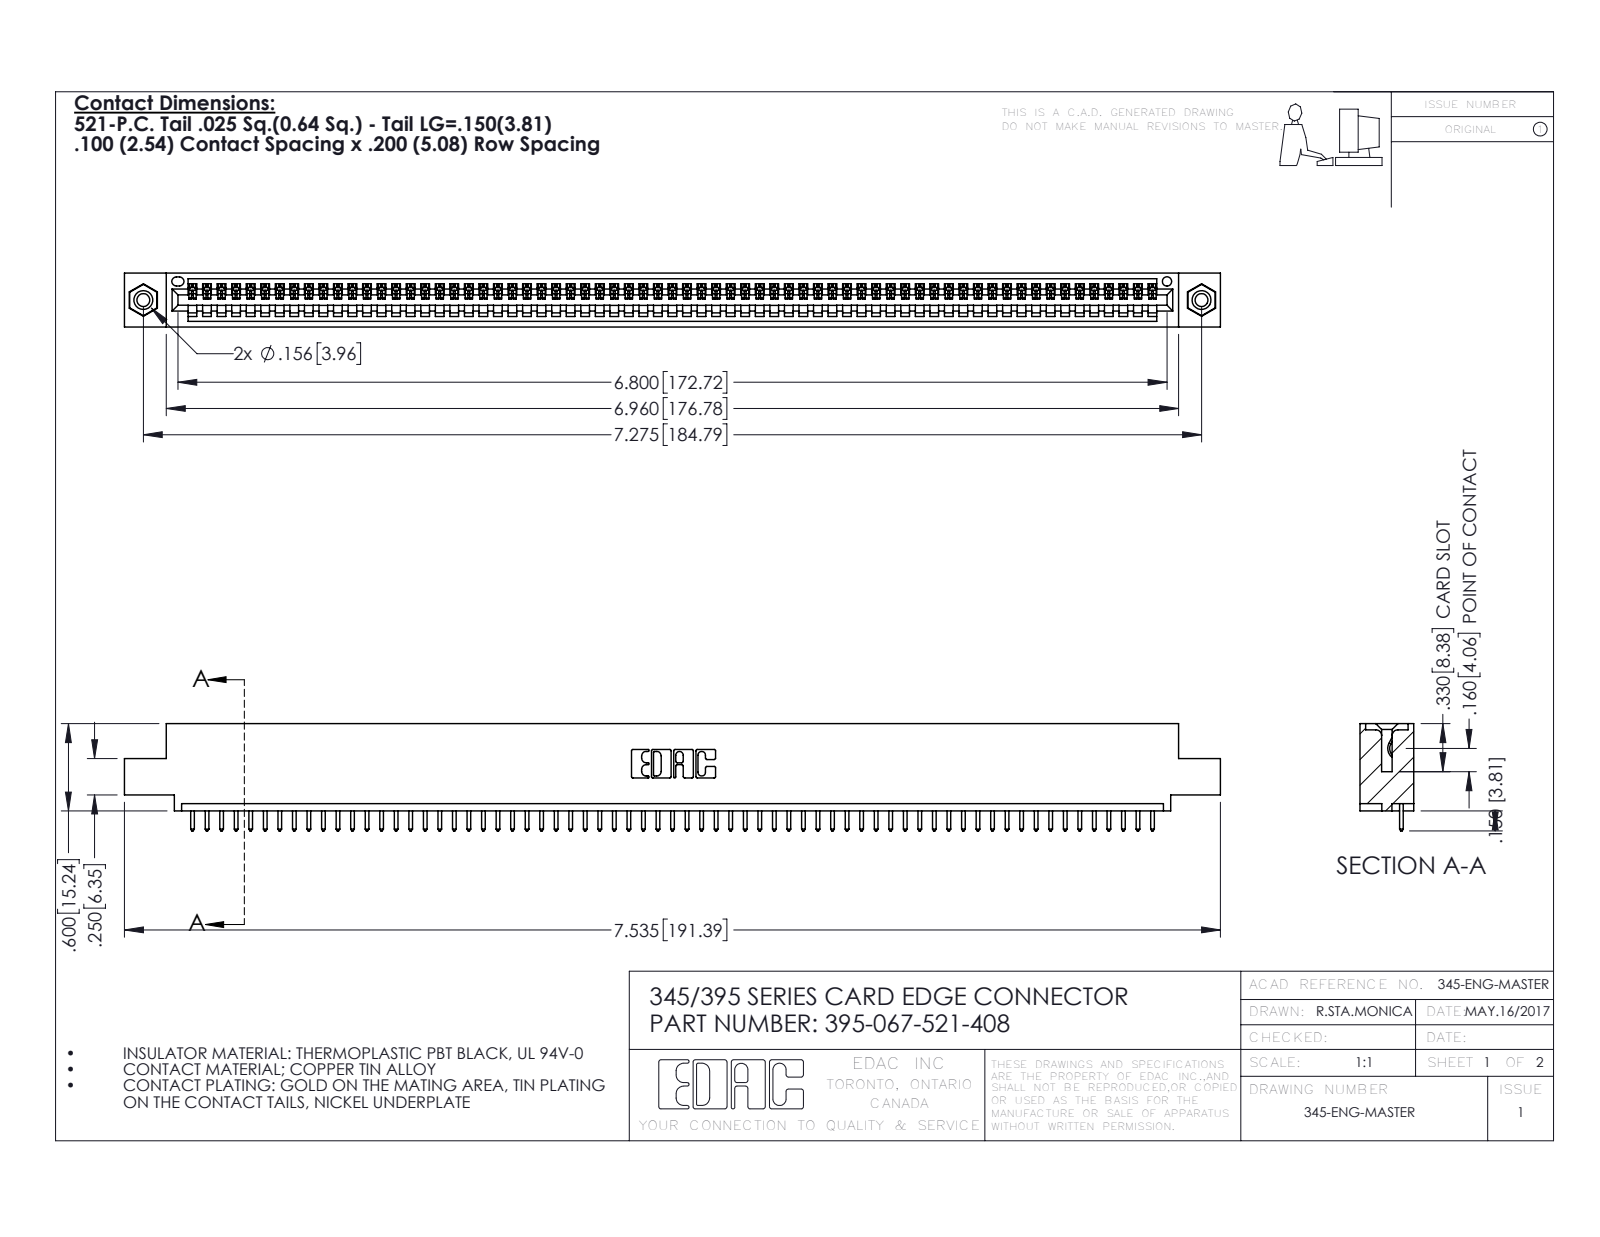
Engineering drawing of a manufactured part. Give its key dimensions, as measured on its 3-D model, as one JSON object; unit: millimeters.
{"part_name": "395-067-521-408; 345-250-001_345-250-003-102; 345-292-001_345-293-121; 345 Part_0.110 Offset - 0.156 Dia-TI", "step_written_by": "SolidWorks 2016 (CONFIG_CONTROL_DESIGN)", "units": "millimeters", "bodies": {"solids": 70, "faces": 4076, "planar": 2796, "cylindrical": 1264, "other": 16}, "overall_size": [191.4, 18.7, 9.4], "volume_mm3": 18110, "surface_area_mm2": 23770, "round_holes": [[2.3, 2], [3.2, 2], [4, 2], [1.6, 1]], "round_bosses_or_shafts": [[3.9, 2]], "partial_cylinders_radius": [[0.2, 134], [0.3, 134], [0.3, 22], [0.2, 6], [0.8, 6], [0.7, 3], [0.8, 2], [1, 2]], "face_to_face_distances": [1.8, 7.6, 9.4, 5.1, 2.5, 6.9, 0.6, 5.7, 3.8, 1.8], "hole_center_spacings": [6.9, 178.8, 184.8]}
